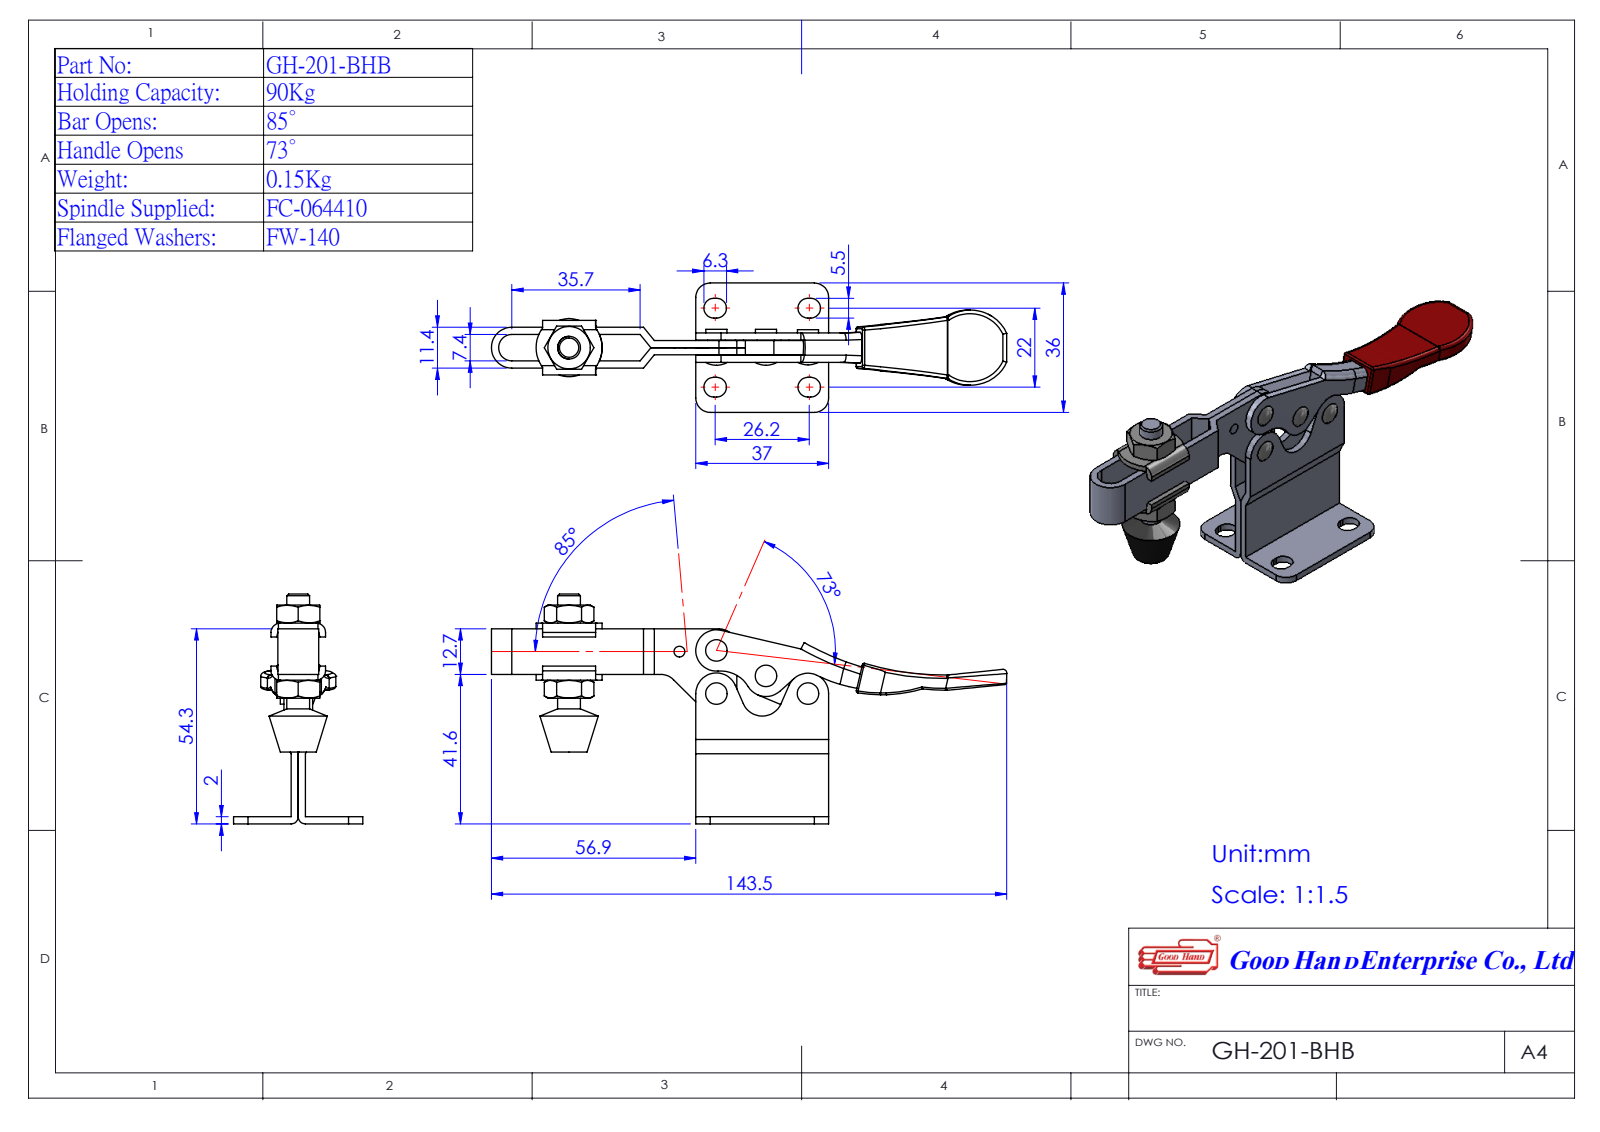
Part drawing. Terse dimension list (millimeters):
name: 1201B08-1^GH-201-BHB(簡化); Group5^GH-201-BHB(簡化); GH-201-BHB(簡化); Group1^組合件13 (+2 more)
written by: SolidWorks 2016 (AUTOMOTIVE_DESIGN)
unit: mm
bodies: 5 solids, 259 faces (118 planar, 116 cylindrical, 25 other)
size: 143.52 × 64 × 36
volume: 22 721 mm³; area: 20 057 mm²
holes: 2× ⌀3.5, 2× ⌀4
bosses: 4× ⌀5.85, 2× ⌀4.85, 2× ⌀3.5, 1× ⌀6.35
rounds: 8× R2.75, 6× R5.75, 4× R1, 4× R2.6, 4× R4, 3× R80, 2× R5, 2× R5.7
face distances: 2, 4, 3.7, 5.7, 7.7, 1.7, 1.6, 7.8, 2.1, 4.1
hole spacings: 12, 12.7, 14.64, 15.5, 25.5, 28.18
